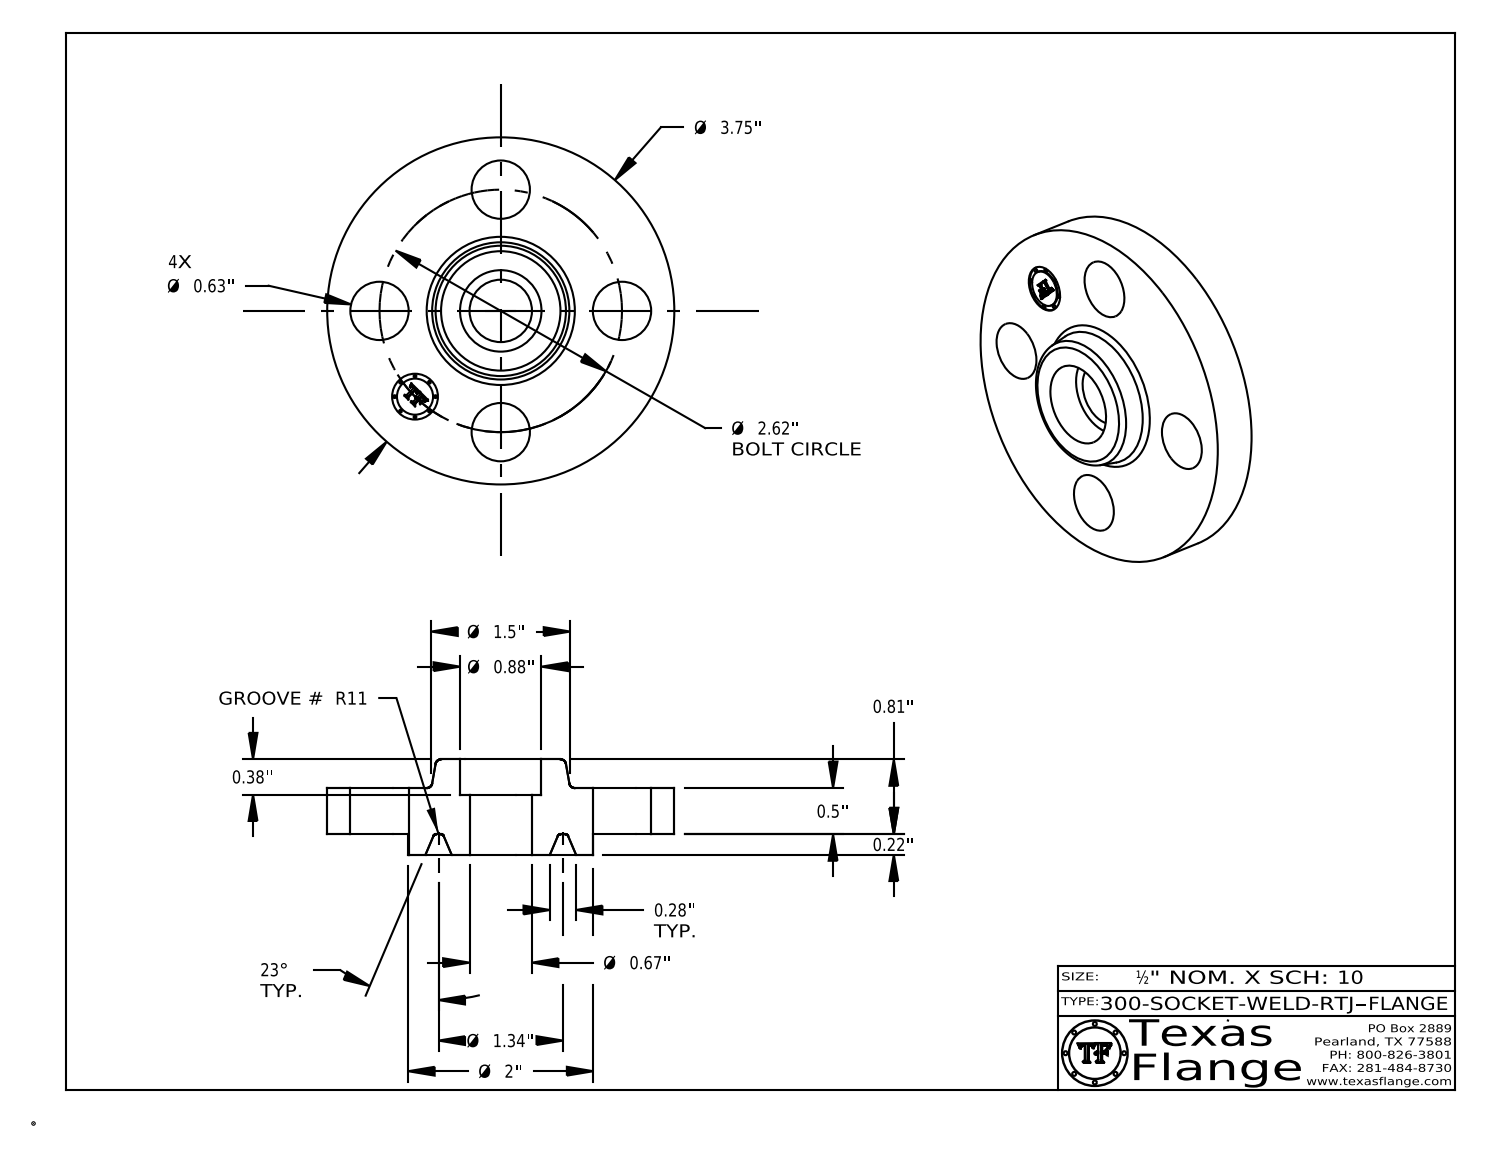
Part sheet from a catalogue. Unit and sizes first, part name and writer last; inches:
Units: inches
Overall size (bounding box): 3.75 × 3.75 × 1.029
Round holes (diameter × count): ⌀0.63 ×4, ⌀0.495 ×1, ⌀0.674 ×1, ⌀0.88 ×1
Round bosses / shafts (diameter × count): ⌀0.03 ×8, ⌀3.75 ×1, ⌀2 ×1, ⌀0.39 ×1
Main face-to-face distances: 0.5, 0.219, 0.719, 1.029, 0.81, 0.31, 0.07, 0.649, 0.43, 0.38
Hole centre spacings: 1.31, 1.852, 1.003, 2.42, 2.62, 1.31
Volume: 5.459 in³ · Surface area: 34.84 in²
Bodies: 1 solid, 426 faces (372 planar, 40 cylindrical, 14 other)
Part name (STEP PRODUCT): 300-SOCKET-WELD-RTJ
STEP written by: CATIA V5 STEP AP214 (AUTOMOTIVE_DESIGN)
